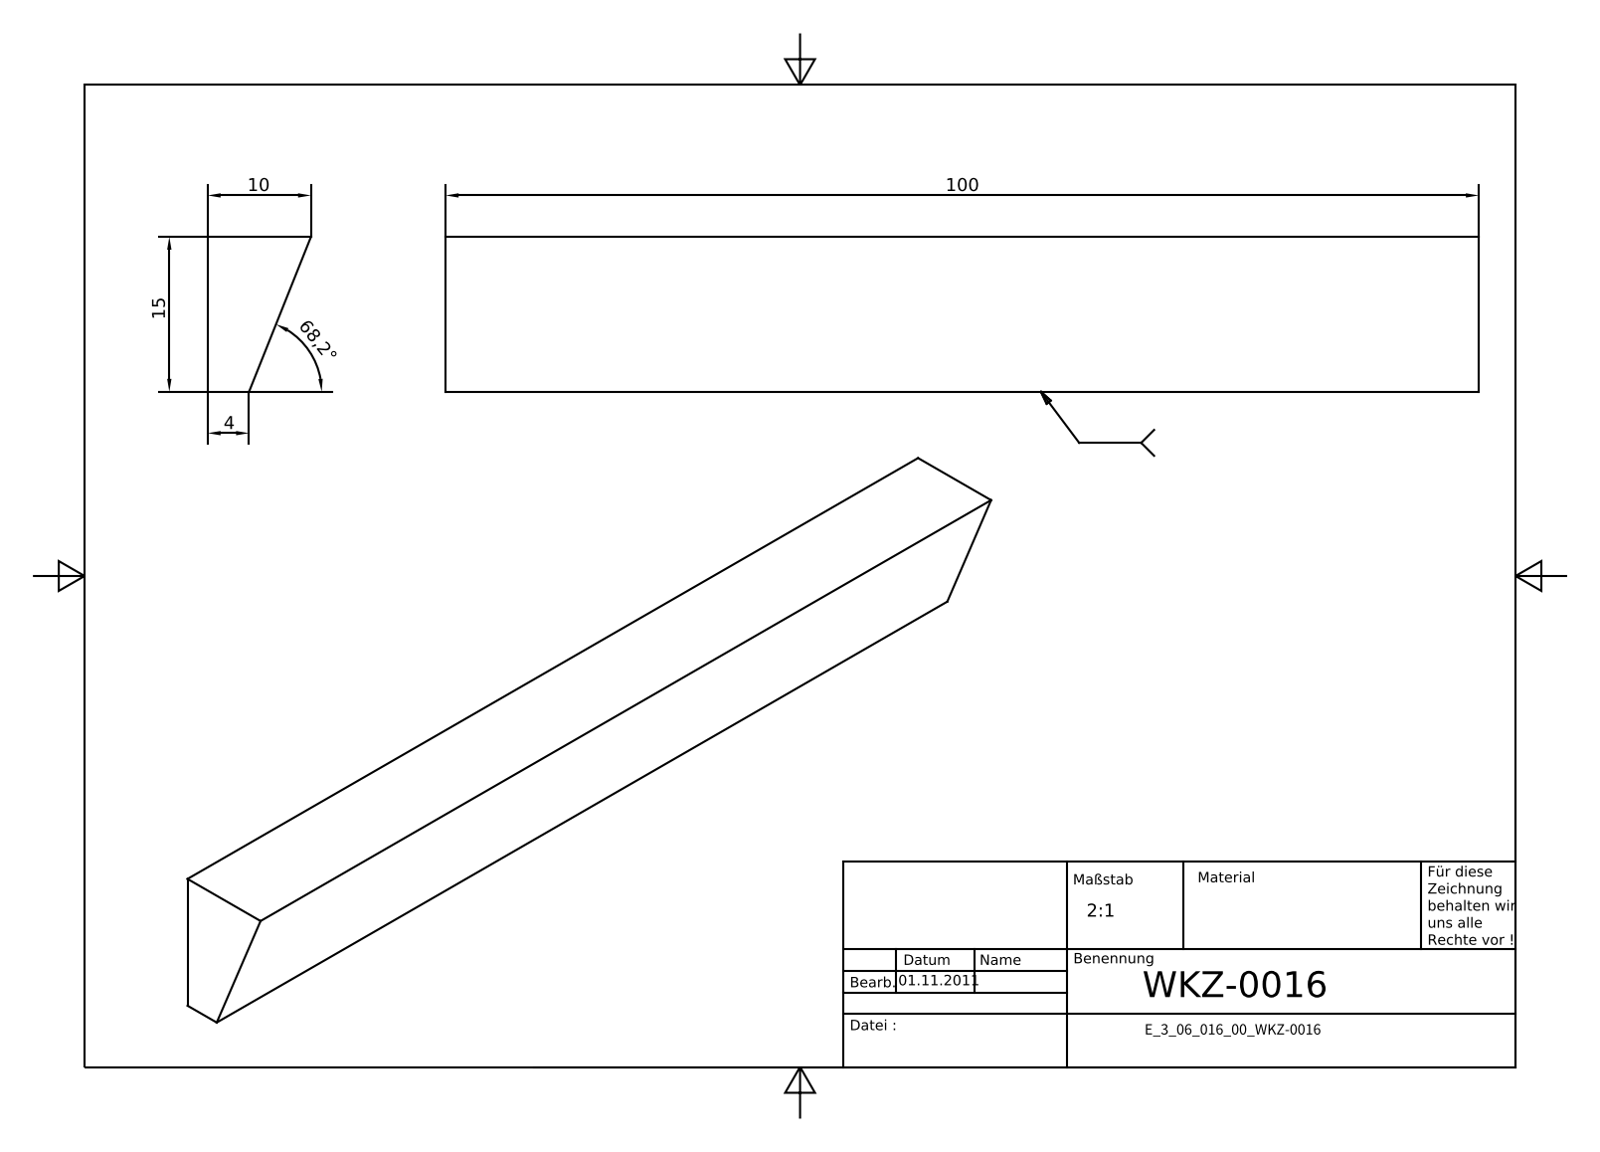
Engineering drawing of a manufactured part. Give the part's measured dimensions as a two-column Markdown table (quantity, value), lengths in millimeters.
| quantity | value |
| --- | --- |
| part name | E_3_01_06_06_00_WKZ-0016 |
| STEP written by | Autodesk Inventor 2021 (AUTOMOTIVE_DESIGN) |
| units | millimeters |
| bodies | 1 solid, 6 faces (6 planar, 0 cylindrical, 0 other) |
| overall size | 100 × 15 × 10 |
| volume | 10 500 mm³ |
| surface area | 4 726 mm² |
| main face-to-face distances | 15, 100 |
